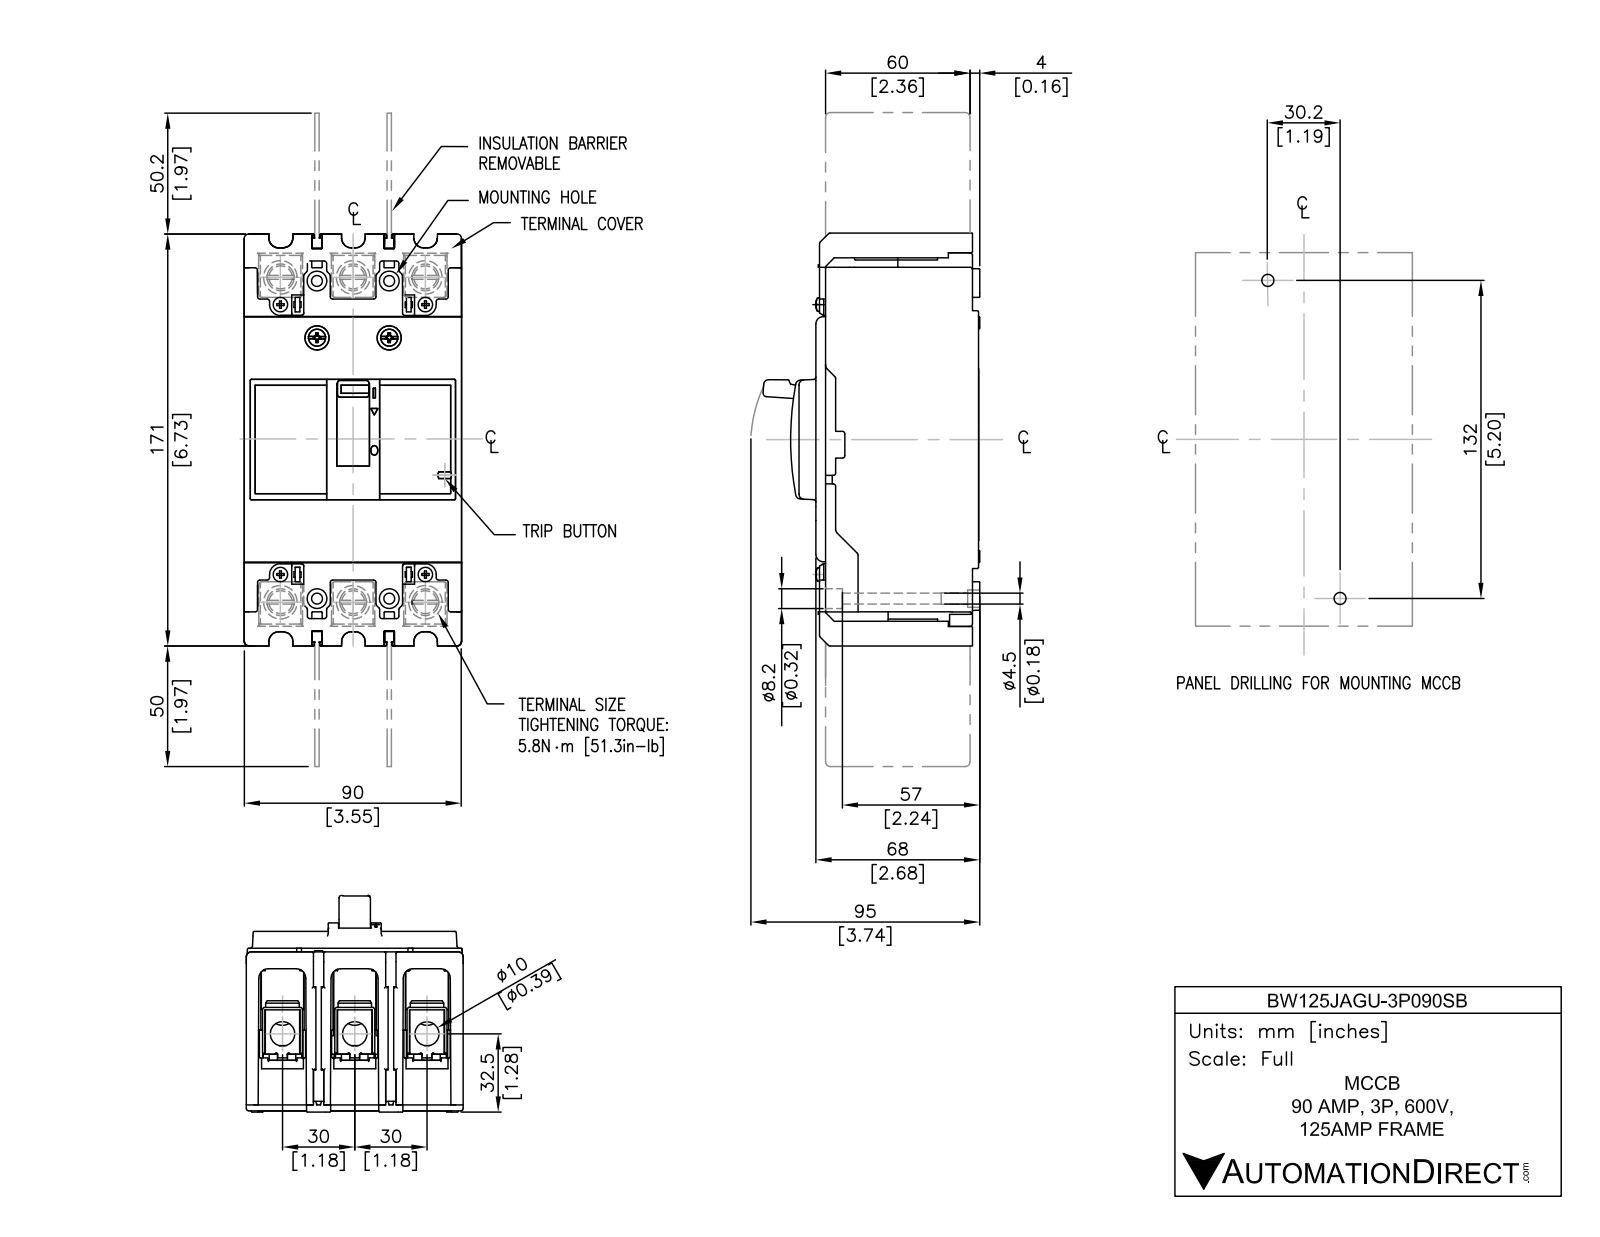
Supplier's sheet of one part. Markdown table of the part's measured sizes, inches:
| quantity | value |
| --- | --- |
| part name | BW125JAGU-3P090SB |
| STEP written by | SolidWorks 2018 (AUTOMOTIVE_DESIGN) |
| units | inches |
| bodies | 14 solids, 452 faces (340 planar, 88 cylindrical, 24 other) |
| overall size | 10.197 × 3.602 × 3.543 |
| volume | 57.4 in³ |
| surface area | 230.3 in² |
| round holes (diameter × count) | 0.315 × 6, 0.177 × 4, 0.323 × 4 |
| round bosses / shafts (diameter × count) | 0.472 × 6 |
| partial cylindrical surfaces (radius × count) | 0.157 × 12, 0.079 × 6, 0.118 × 6 |
| main face-to-face distances | 1.181, 1.11, 1.252, 2.291, 2.433, 0.142, 3.543, 0.236, 2.402, 1.039 |
| hole center spacings | 0.593, 5.289, 1.181, 1.772, 5.444, 5.546, 5.315, 2.362 |
